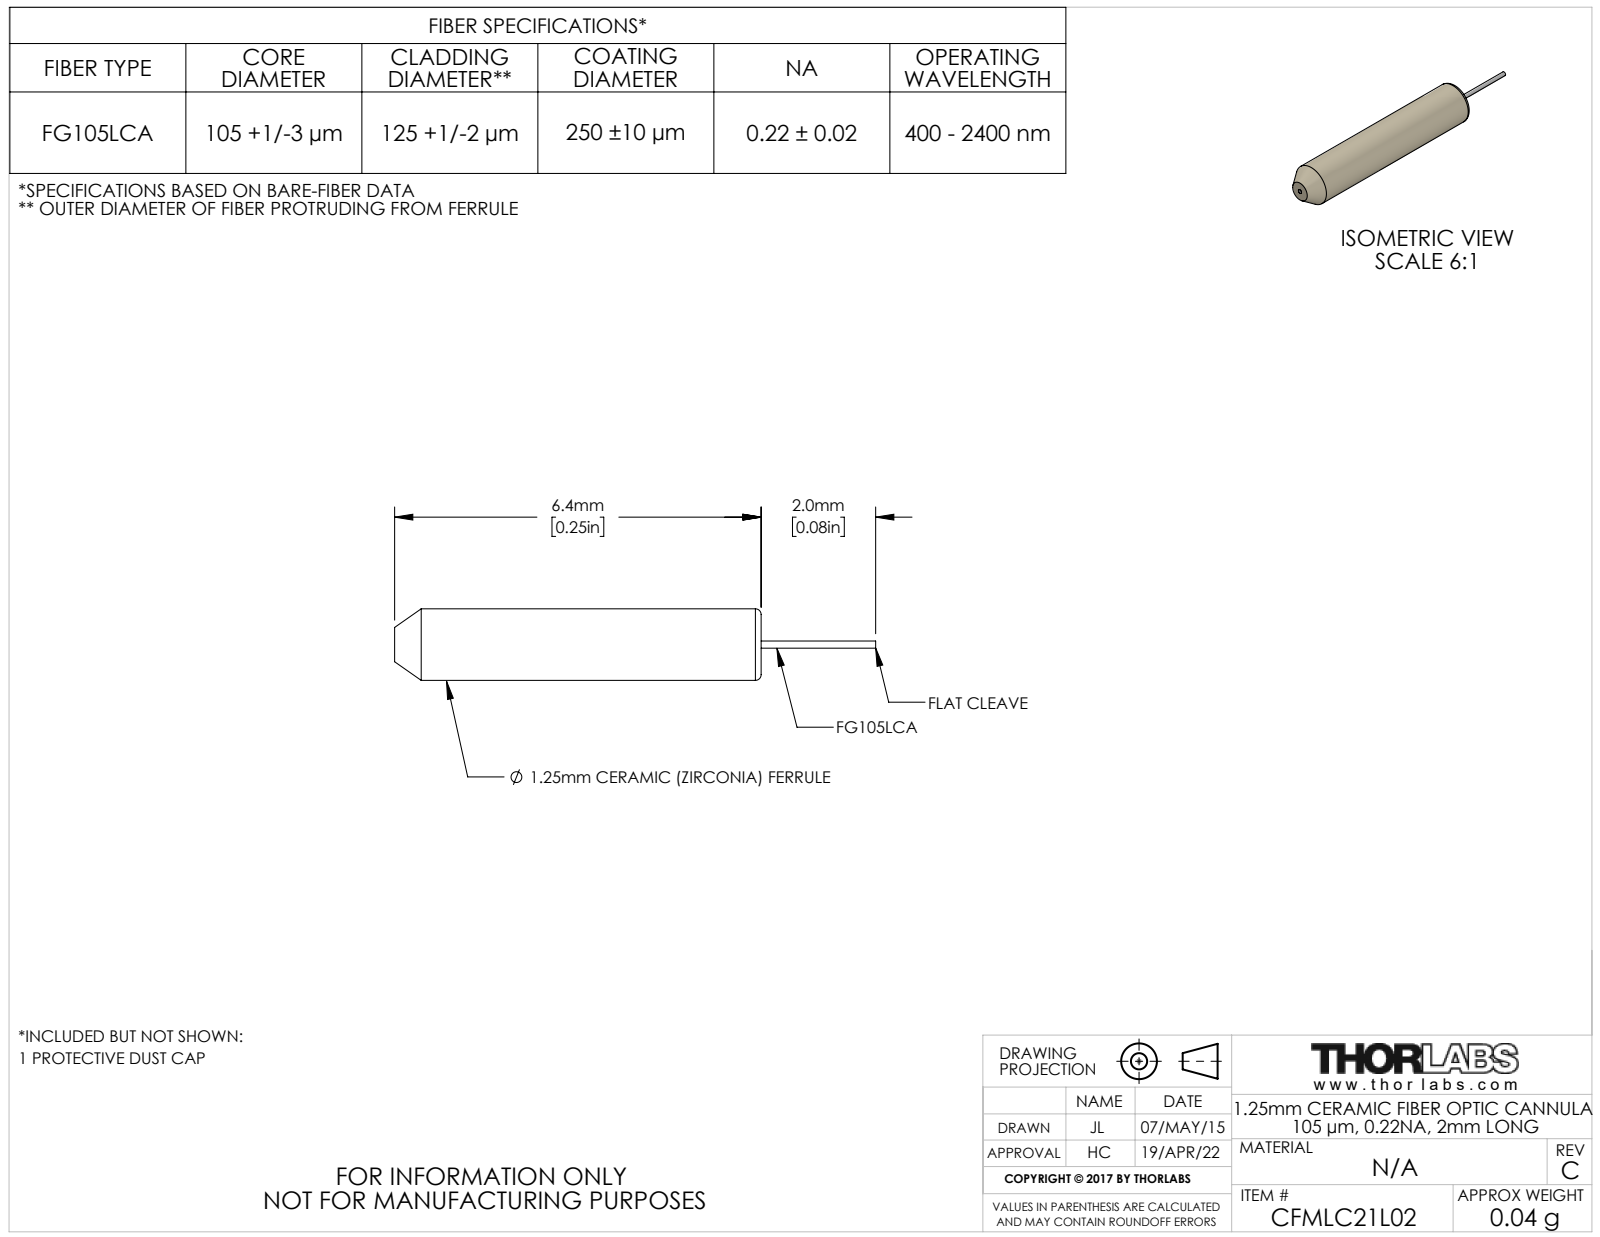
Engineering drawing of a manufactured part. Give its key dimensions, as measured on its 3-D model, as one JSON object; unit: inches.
{"part_name": "TTN041719-E0W", "step_written_by": "SolidWorks 2014 (CONFIG_CONTROL_DESIGN)", "units": "inches", "bodies": {"solids": 2, "faces": 18, "planar": 4, "cylindrical": 6, "other": 8}, "overall_size": [0.331, 0.049, 0.049], "round_bosses_or_shafts": [[0.049, 1]], "face_to_face_distances": [0.252, 0.331, 0.079]}
